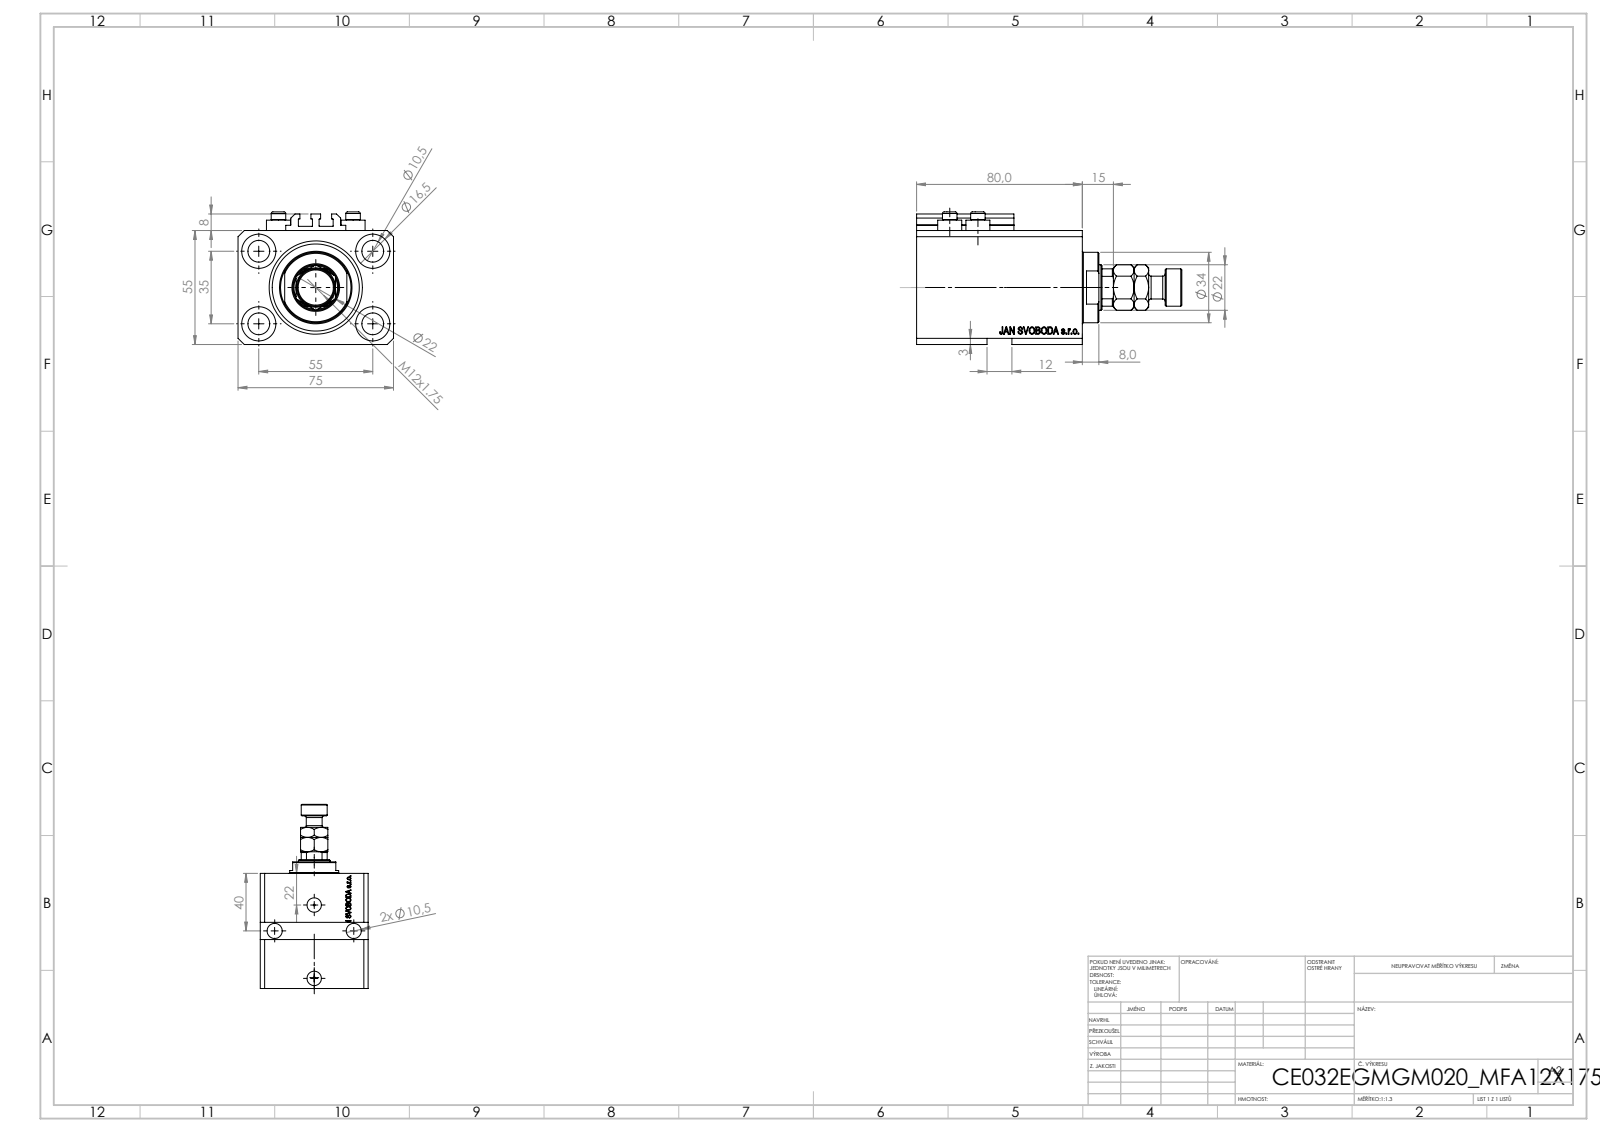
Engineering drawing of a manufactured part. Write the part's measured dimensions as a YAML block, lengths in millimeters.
part_name: "V250CE_E_Body; MFA; V250CE_C_VCP; V250CE_VC_E (+1 more)"
step_written_by: "SolidWorks 2019 (CONFIG_CONTROL_DESIGN)"
units: millimeters
bodies: {solids: 9, faces: 1116, planar: 530, cylindrical: 130, other: 456}
overall_size: [128, 75, 64]
volume: 291962
surface_area: 77160
round_holes:
  - {diameter: 10.5, count: 7}
  - {diameter: 1.25, count: 4}
  - {diameter: 4, count: 4}
  - {diameter: 16.5, count: 4}
  - {diameter: 10, count: 2}
  - {diameter: 13.16, count: 2}
  - {diameter: 20, count: 2}
  - {diameter: 22, count: 1}
  - {diameter: 32, count: 1}
  - {diameter: 45, count: 1}
round_bosses_or_shafts:
  - {diameter: 11.6, count: 4}
  - {diameter: 7, count: 4}
  - {diameter: 34, count: 1}
  - {diameter: 18, count: 1}
  - {diameter: 11, count: 1}
partial_cylinders:
  - {radius: 0.2, count: 10}
  - {radius: 10.5, count: 1}
face_to_face_distances: [55, 75, 15, 65, 80, 3, 55.1, 9.9, 70.1, 54]
hole_center_spacings: [32.6, 55, 13.6, 14.09, 19.89, 20.12, 25.81, 28.48]
